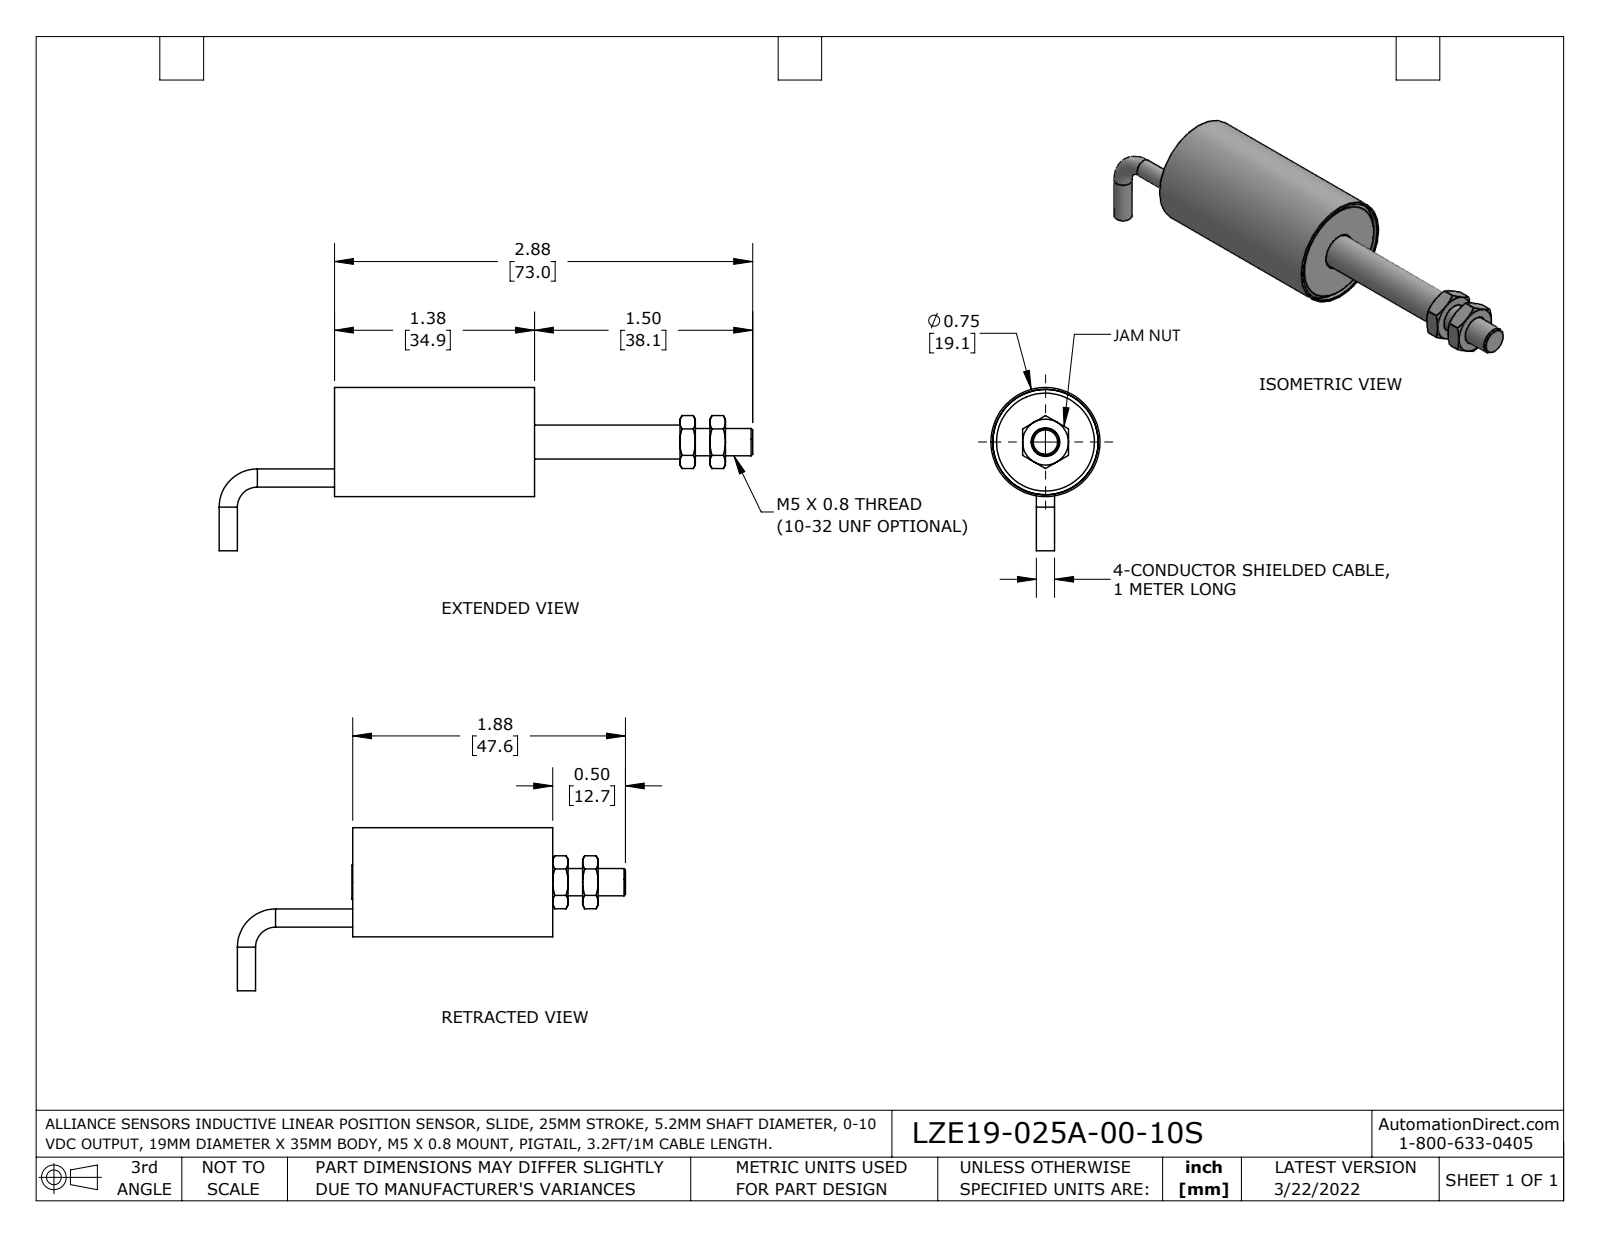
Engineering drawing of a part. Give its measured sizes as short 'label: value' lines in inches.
name: 3120-0006-06_-01-0Y; 3120-0007-ZY; 3300-0008-06_-01; 3120-0007-ZY_with slot (+6 more)
written by: SolidWorks 2021 (AUTOMOTIVE_DESIGN)
unit: in
bodies: 10 solids, 137 faces (42 planar, 44 cylindrical, 51 other)
size: 3.668 × 1.121 × 0.75
volume: 0.3 in³; area: 15.45 in²
holes: 1× ⌀0.165, 1× ⌀0.188, 1× ⌀0.197, 1× ⌀0.234, 1× ⌀0.281, 1× ⌀0.68, 1× ⌀0.725
bosses: 2× ⌀0.125, 1× ⌀0.75, 1× ⌀0.723, 1× ⌀0.278, 1× ⌀0.187
rounds: 1× R0.052
face distances: 0.06, 1.295, 0.08, 1.235, 1.355, 0.315, 0.206, 0.106, 0.374, 0.1
